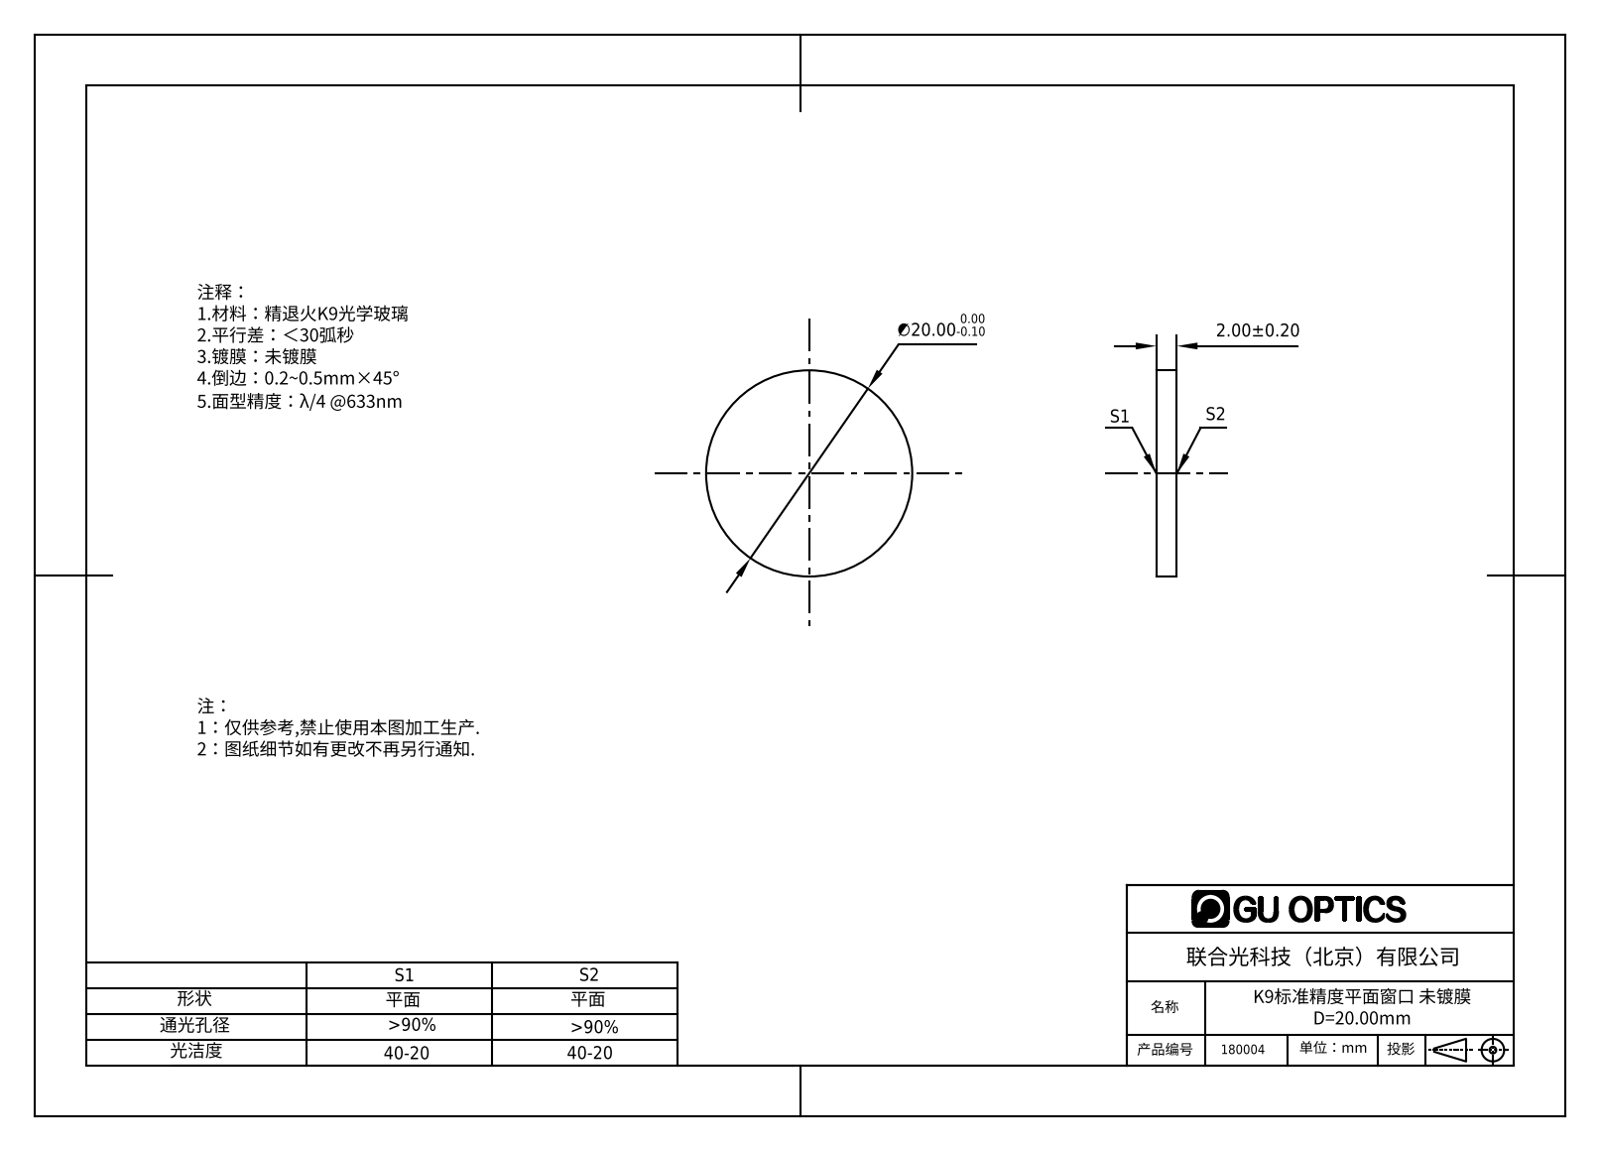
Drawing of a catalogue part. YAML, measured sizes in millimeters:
part_name: "180004"
step_written_by: "SolidWorks 2016 (AUTOMOTIVE_DESIGN)"
units: millimeters
bodies: {solids: 1, faces: 4, planar: 2, cylindrical: 2, other: 0}
overall_size: [20, 20, 2]
volume: 628
surface_area: 754
round_bosses_or_shafts:
  - {diameter: 20, count: 1}
face_to_face_distances: [2]
